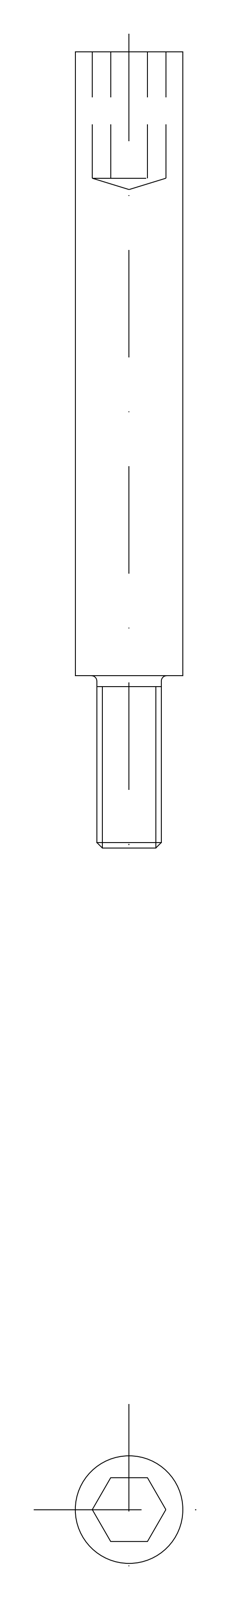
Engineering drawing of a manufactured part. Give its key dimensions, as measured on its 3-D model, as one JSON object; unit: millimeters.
{"step_written_by": "THINKDESIGN (CONFIG_CONTROL_DESIGN)", "units": "millimeters", "bodies": {"solids": 1, "faces": 13, "planar": 10, "cylindrical": 2, "other": 1}, "overall_size": [74, 10, 10], "volume_mm3": 4647, "surface_area_mm2": 2517, "round_bosses_or_shafts": [[10, 1], [6, 1]], "face_to_face_distances": [5.92, 58, 46.23, 11.77, 16, 62.23, 74]}
